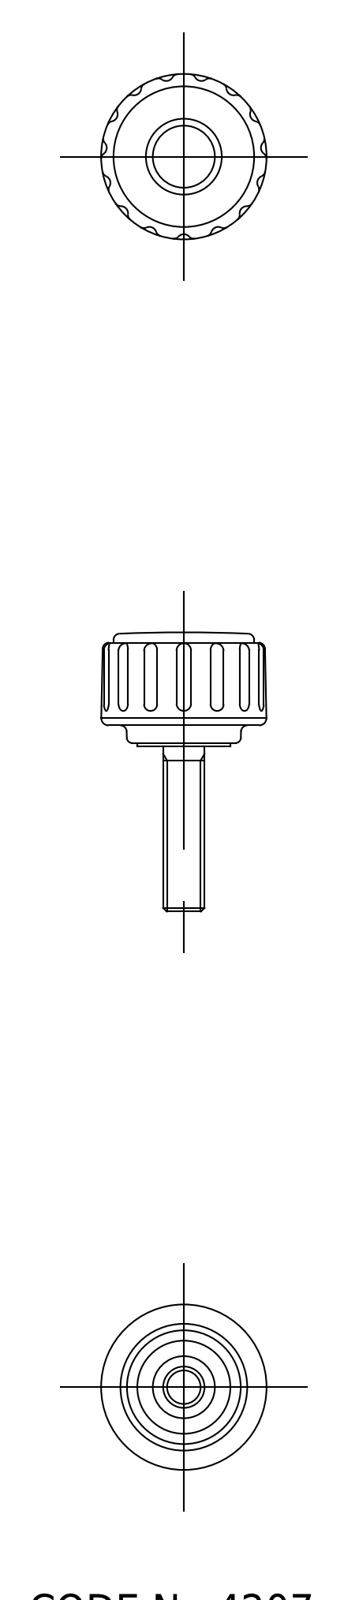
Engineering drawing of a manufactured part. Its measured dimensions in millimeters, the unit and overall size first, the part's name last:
Units: millimetres
Overall size (bounding box): 26.95 × 16.12 × 15.97
Volume: 2 021 mm³ · Surface area: 1 322 mm²
Bodies: 2 solids, 68 faces (0 planar, 0 cylindrical, 68 other)
Part name (STEP PRODUCT): screw; knob; KDM_16_M4_16_2249_36
STEP written by: CADfix (AUTOMOTIVE_DESIGN)
